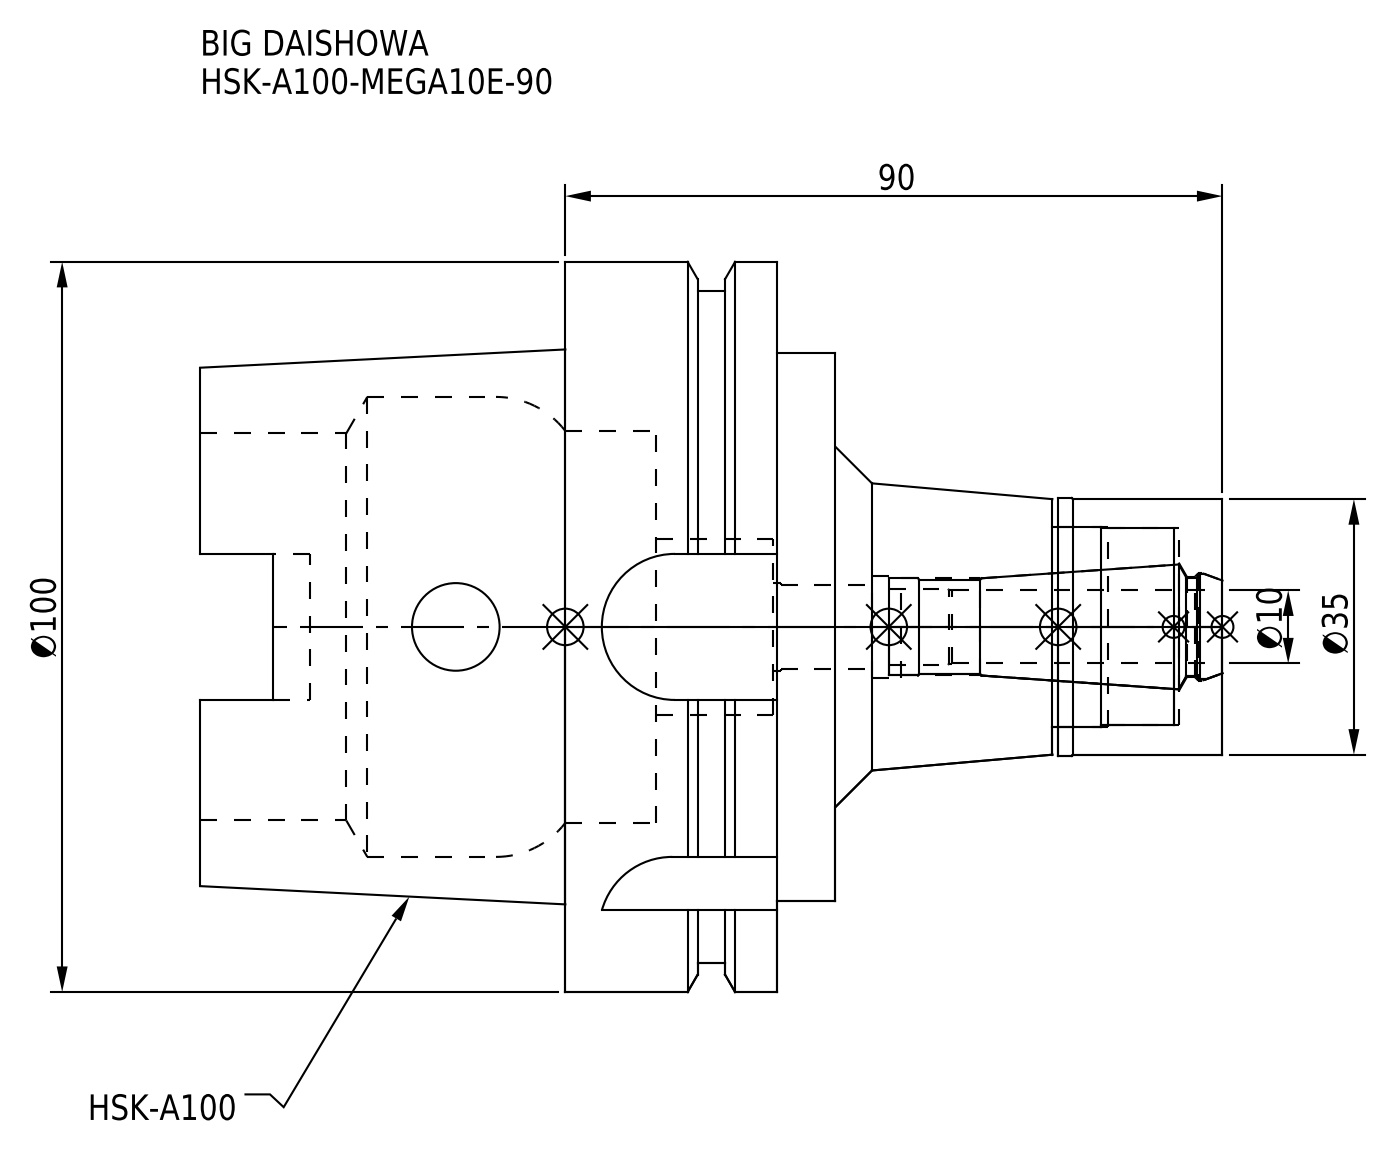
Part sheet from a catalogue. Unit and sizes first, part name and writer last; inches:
Units: inches
Overall size (bounding box): 5.512 × 3.937 × 3.937
Round holes (diameter × count): ⌀0.472 ×2, ⌀0.453 ×1, ⌀0.524 ×1, ⌀0.543 ×1, ⌀0.547 ×1, ⌀0.579 ×1, ⌀0.945 ×1, ⌀1.063 ×1, ⌀1.083 ×1, ⌀2.087 ×1, ⌀2.118 ×1, ⌀2.48 ×1
Round bosses / shafts (diameter × count): ⌀3.937 ×1, ⌀3.622 ×1, ⌀2.953 ×1, ⌀1.39 ×1, ⌀1.378 ×1
Partial cylindrical surfaces — rounded edges, fillets, slot ends (radius × count): R0.192 ×4, R0.394 ×4
Main face-to-face distances: 1.142, 1.457, 0.315, 0.967, 0.652, 0.49, 3.11, 3.425, 2.459, 1.969
Volume: 20.5 in³ · Surface area: 99.43 in²
Bodies: 2 solids, 126 faces (42 planar, 56 cylindrical, 28 other)
Part name (STEP PRODUCT): HSK-A100-MEGA10E-90; HSK-A100-MEGA10E-90_1.stp; HSK-A100-MEGA10E-90-100.stp; MEN10_1.stp (+3 more)
STEP written by: SolidWorks 2019 (CONFIG_CONTROL_DESIGN)
